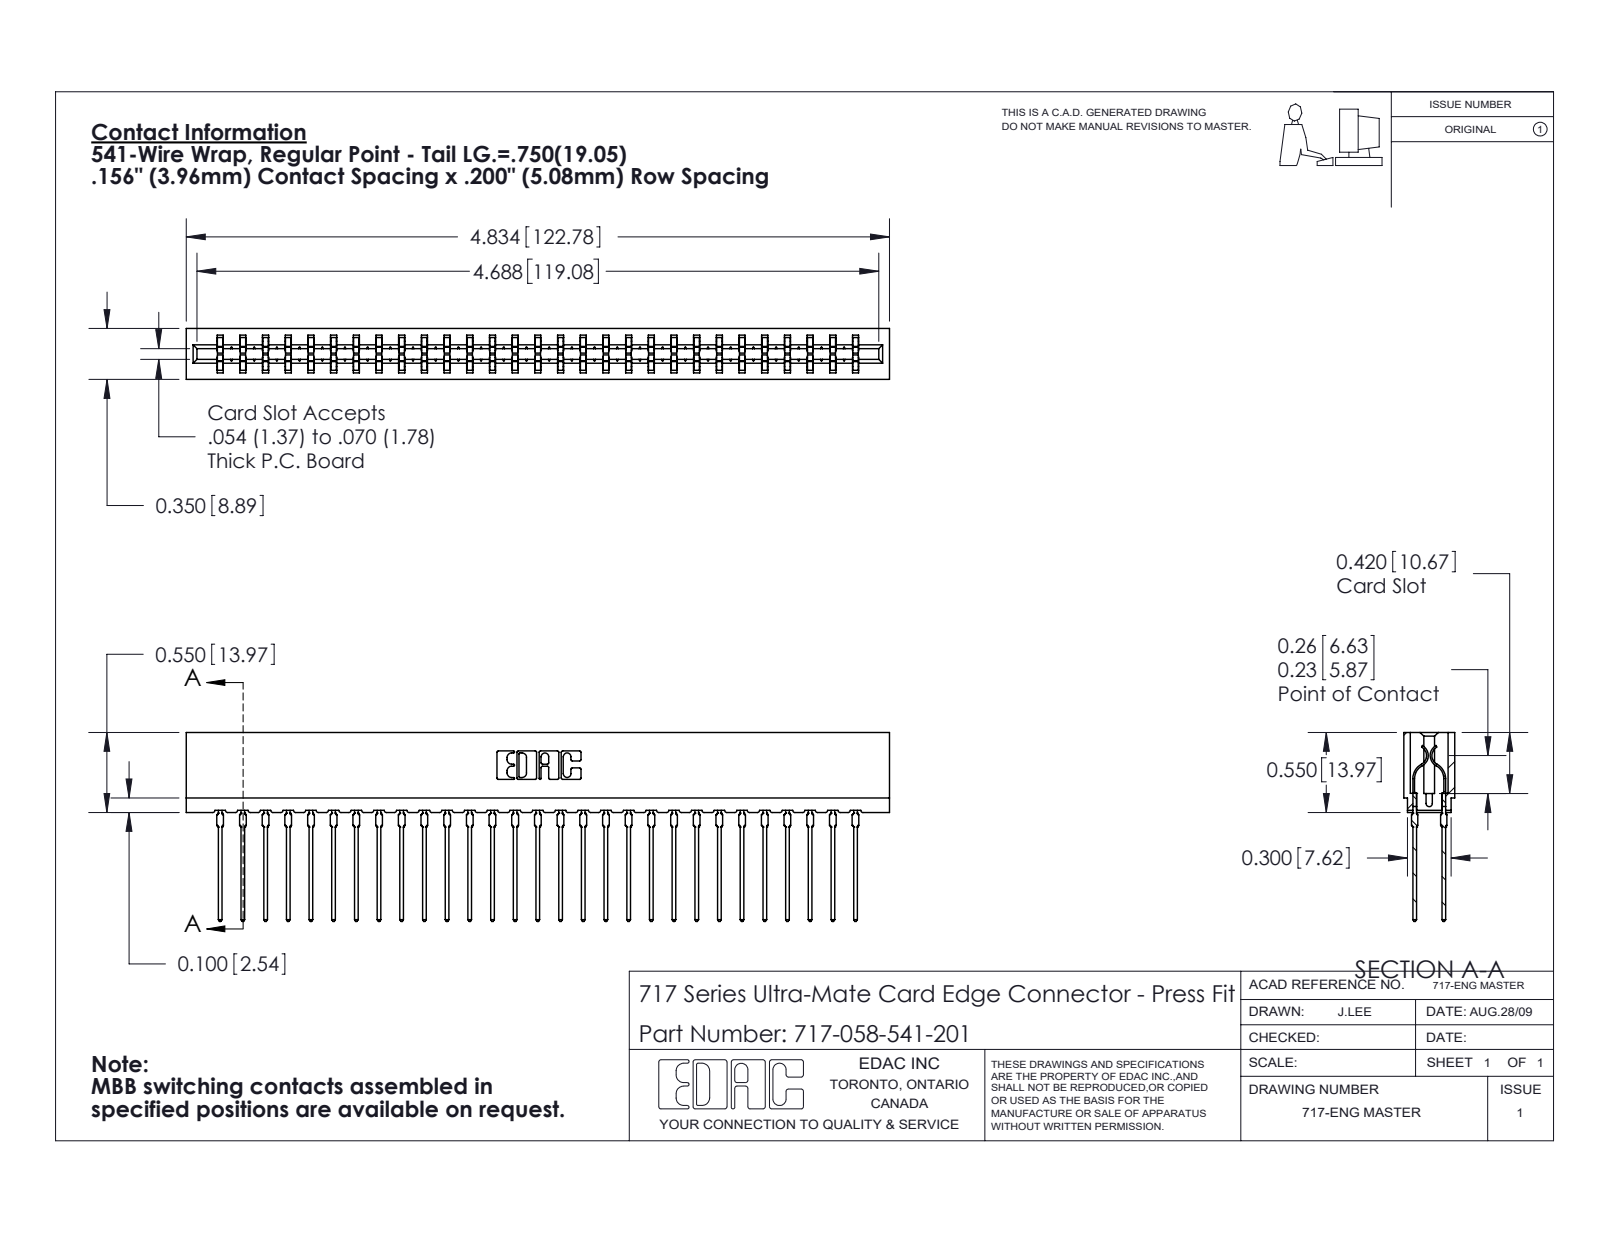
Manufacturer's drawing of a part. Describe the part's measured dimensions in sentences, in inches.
The part is named "717 Part_Insulator Option - 06; 717-058-541-201; 745-292-001_541". Its 3-D file was written by "SolidWorks 2020 (CONFIG_CONTROL_DESIGN)". It is 59 solids with 5314 faces: 2751 planar, 1055 cylindrical and 1508 other. Overall it measures 4.834 by 1.299 by 0.35 inches. Its volume is 0.67 cubic inches and its surface area 27.76 square inches. Partial cylindrical surfaces (rounded edges, fillets, slot ends): 116 of radius 0.021, 58 of radius 0.015, 22 of radius 0.01, 8 of radius 0.005, 8 of radius 0.011, 6 of radius 0.007, 6 of radius 0.031, 3 of radius 0.026. The main face-to-face distances are 0.212, 0.138, 0.35, 0.063, 0.287, 0.076, 0.149, 0.087, 0.263, 0.025.
